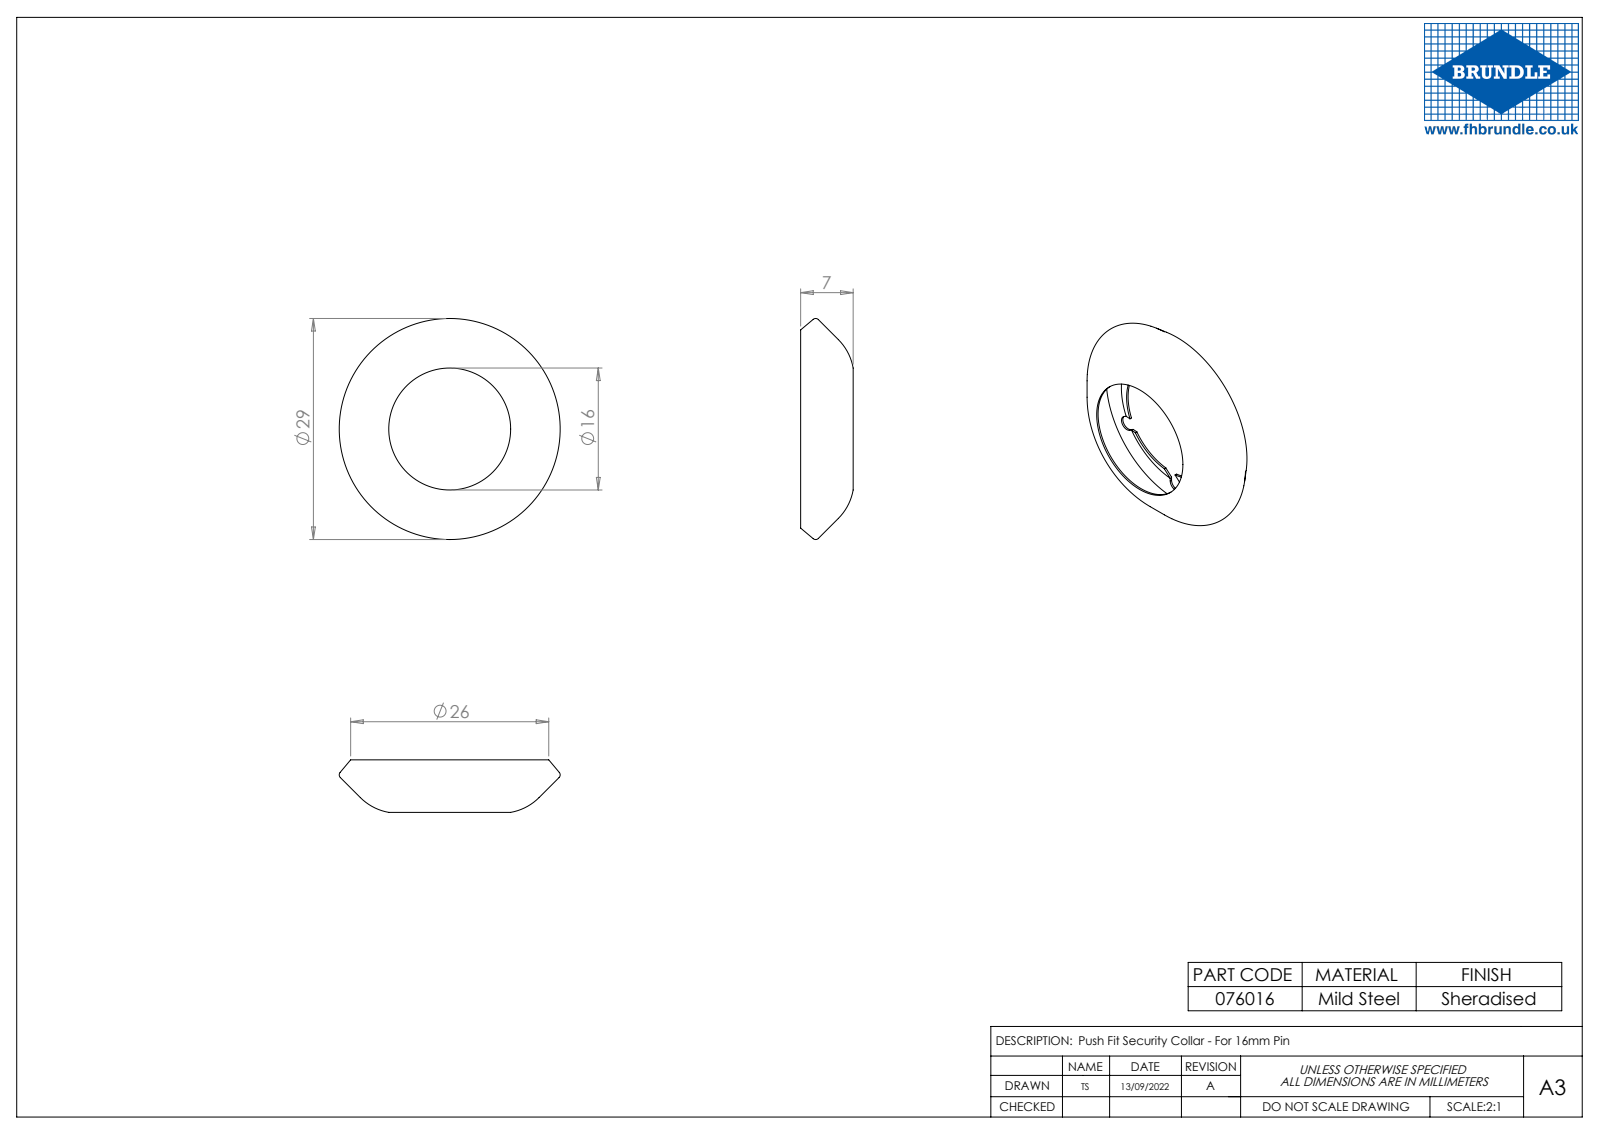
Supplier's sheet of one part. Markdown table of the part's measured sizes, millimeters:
| quantity | value |
| --- | --- |
| part name | 076019 |
| STEP written by | SolidWorks 2023 (CONFIG_CONTROL_DESIGN) |
| units | millimeters |
| bodies | 1 solid, 78 faces (33 planar, 17 cylindrical, 28 other) |
| overall size | 38 × 38 × 7 |
| volume | 3 231 mm³ |
| surface area | 3 270 mm² |
| round holes (diameter × count) | 16 × 1 |
| partial cylindrical surfaces (radius × count) | 1 × 6 |
| main face-to-face distances | 7, 6.75, 5.93, 5.68, 1.07, 2 |
